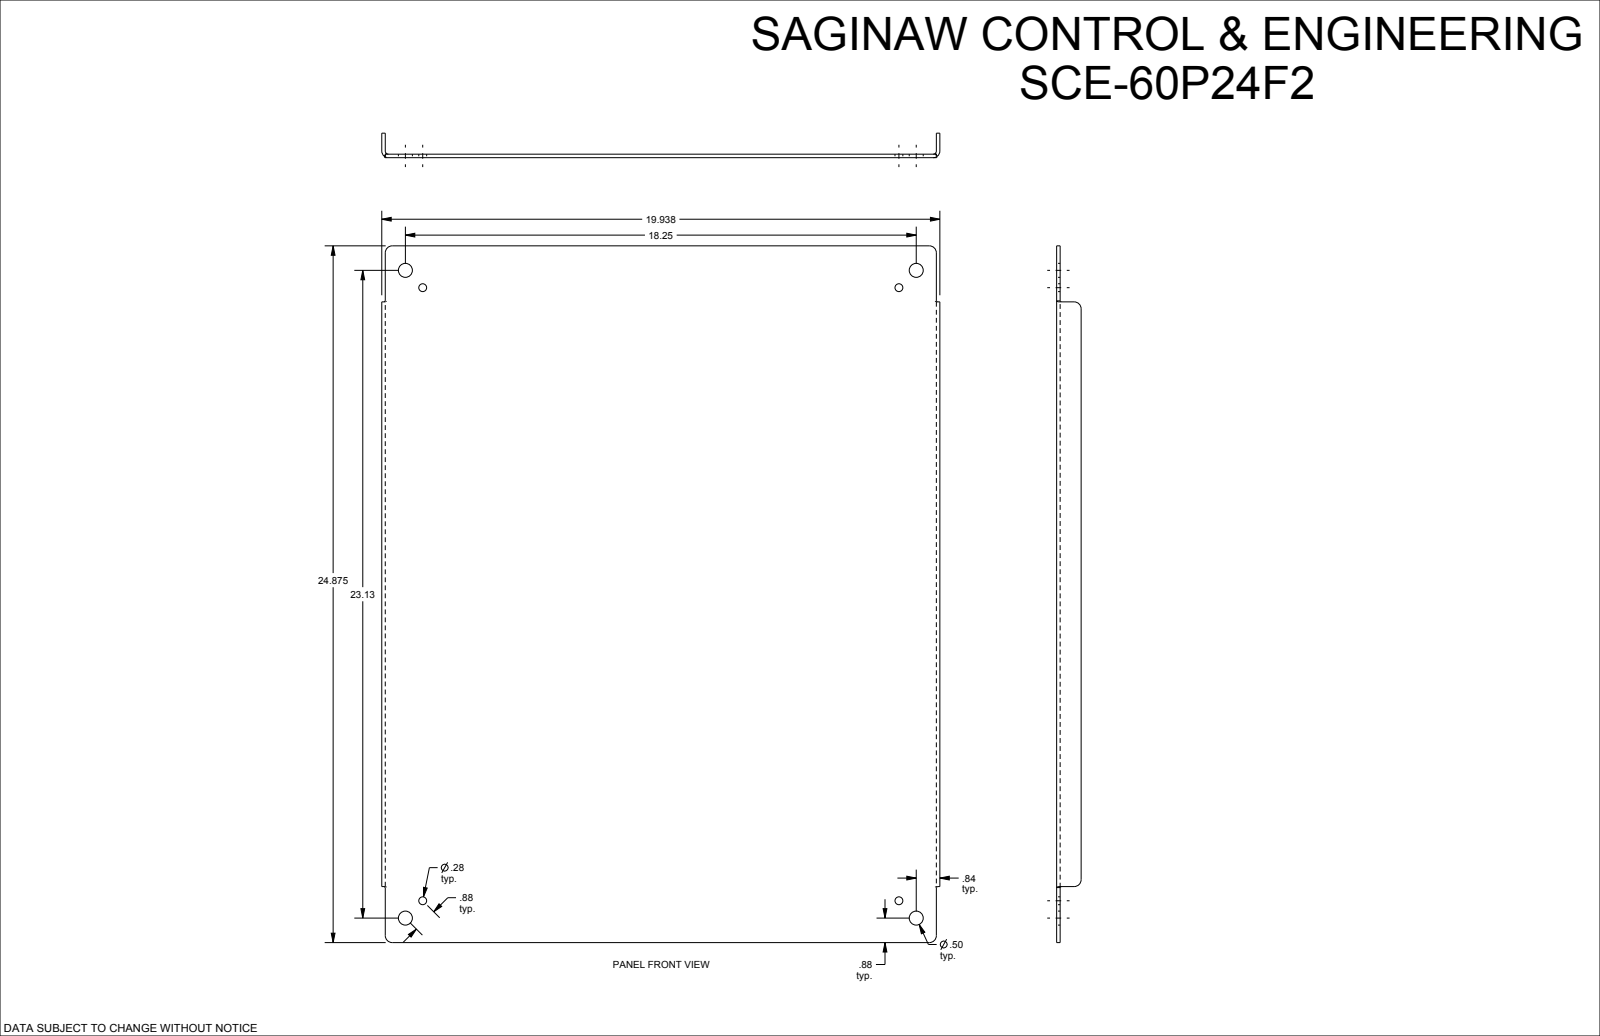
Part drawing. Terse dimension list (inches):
name: SCE-60P24F2
written by: SolidWorks 2019 (CONFIG_CONTROL_DESIGN)
unit: in
bodies: 1 solid, 50 faces (18 planar, 20 cylindrical, 12 other)
size: 24.875 × 19.938 × 0.875
volume: 65.25 in³; area: 1 057 in²
holes: 4× ⌀0.281, 4× ⌀0.5
rounds: 6× R0.25, 2× R0.112, 2× R0.237
face distances: 0.125, 0.125, 19.813, 19.687, 19.938, 0.75, 0.875, 24.875, 2, 22.875
hole spacings: 0.875, 17.642, 22.515, 28.59, 17.013, 18.25, 21.887, 23.125
